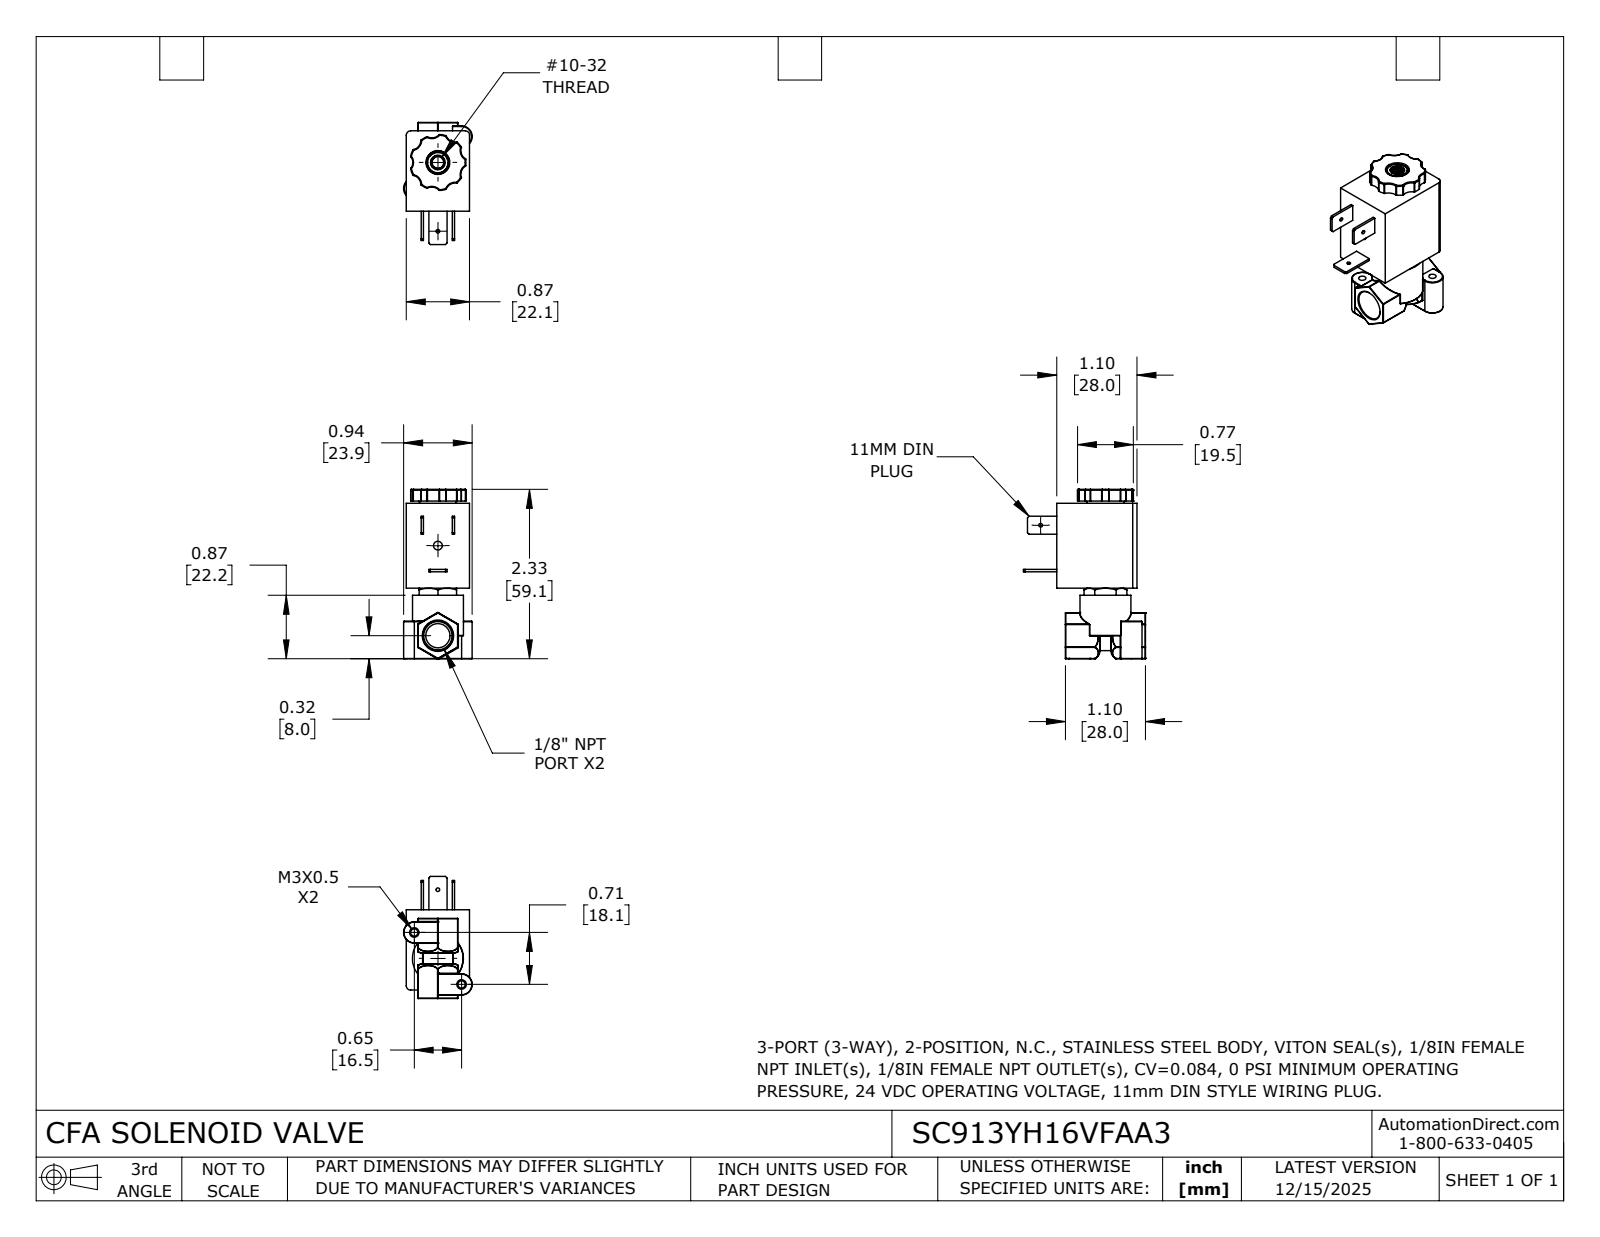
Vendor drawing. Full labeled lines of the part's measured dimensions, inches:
Part name (STEP PRODUCT): SC913YH16VFAA3
STEP written by: SolidWorks 2024 (CONFIG_CONTROL_DESIGN)
Units: inches
Bodies: 1 solid, 363 faces (70 planar, 142 cylindrical, 151 other)
Overall size (bounding box): 2.328 × 1.678 × 0.942
Volume: 1.573 in³ · Surface area: 13.88 in²
Round holes (diameter × count): ⌀0.05 ×2, ⌀0.1 ×2, ⌀0.12 ×1, ⌀0.16 ×1, ⌀0.327 ×1, ⌀0.332 ×1
Round bosses / shafts (diameter × count): ⌀0.7 ×1, ⌀0.315 ×1
Partial cylindrical surfaces — rounded edges, fillets, slot ends (radius × count): R0.004 ×29, R0.01 ×18, R0.008 ×12, R0.133 ×7, R0.017 ×2, R0.06 ×2, R0.132 ×2, R0.146 ×2
Main face-to-face distances: 0.87, 1.104, 1.167, 0.548, 1.357, 0.19, 0.161, 0.709, 0.971, 2.138
Hole centre spacings: 0.483, 0.672, 0.945, 0.965, 1.238, 1.342
